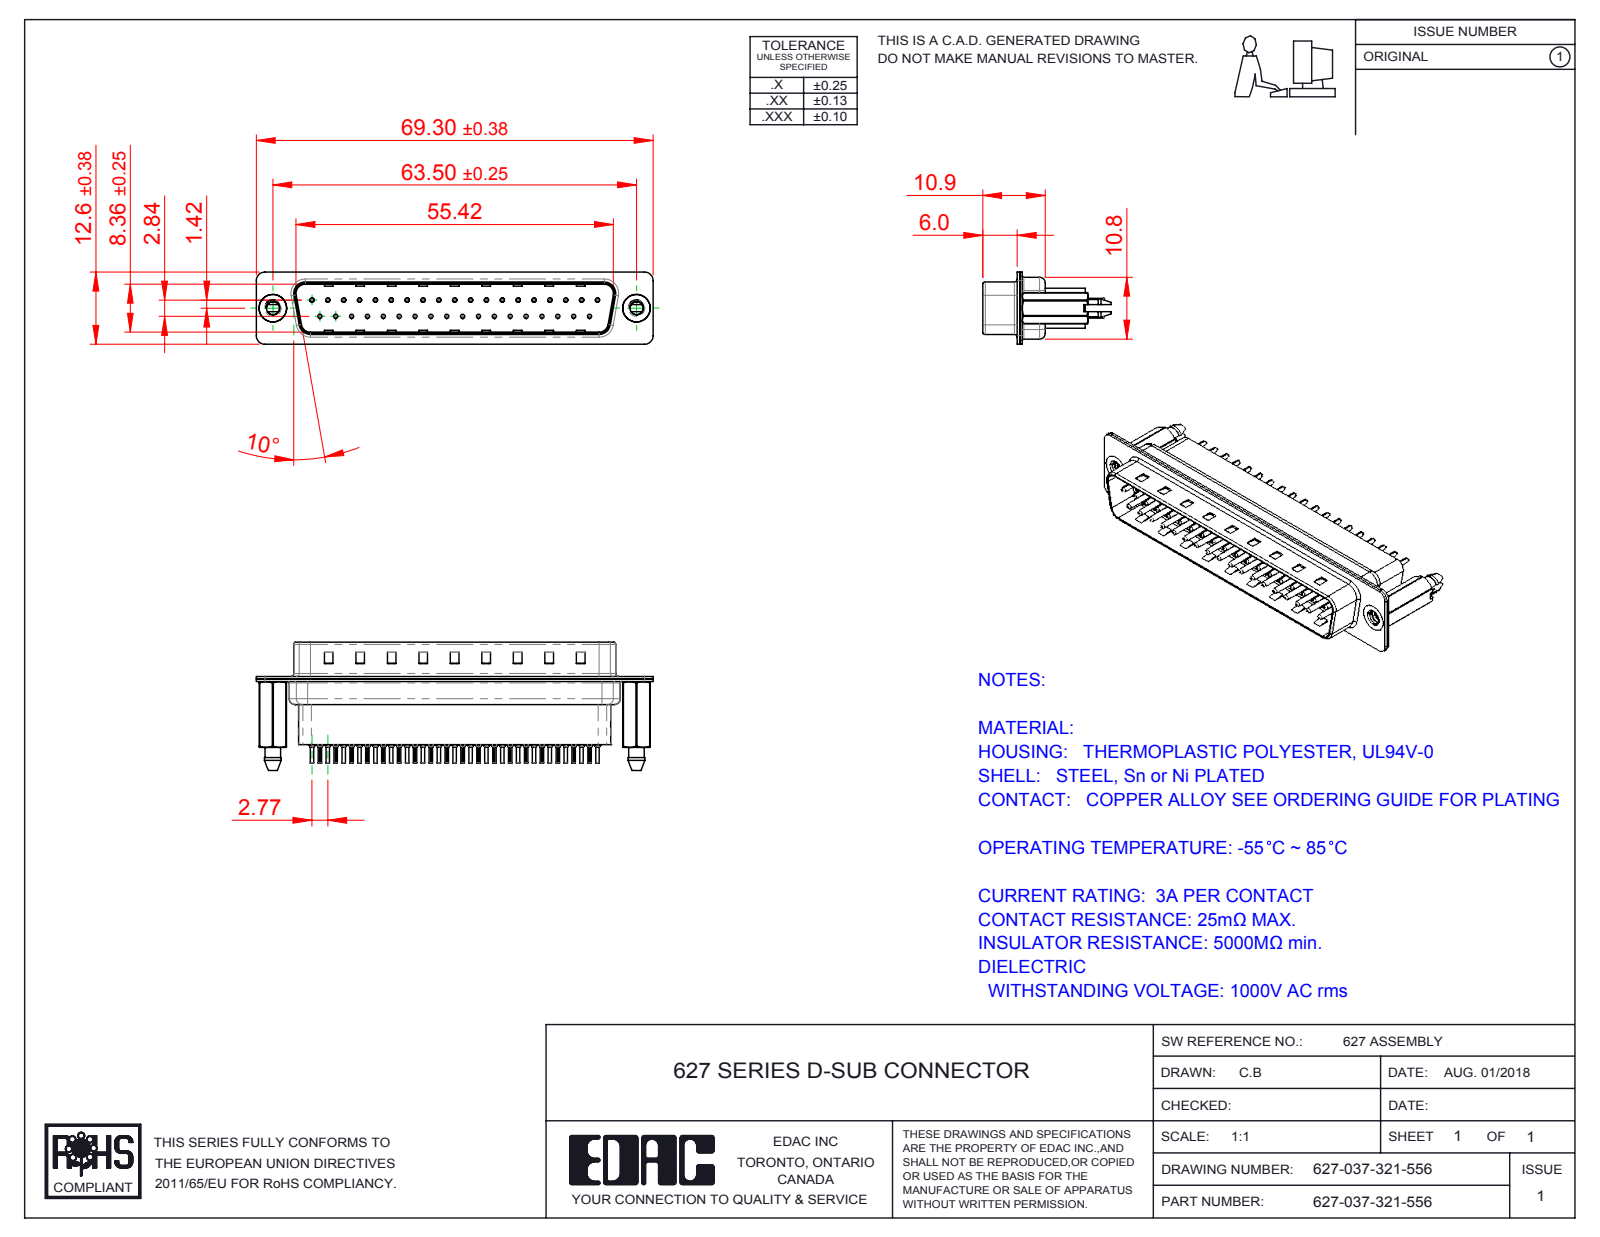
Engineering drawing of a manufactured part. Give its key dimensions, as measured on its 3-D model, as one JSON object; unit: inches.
{"part_name": "627 4-40 Threaded Boardlock_HP; 627 Contact Row 2_21H; 627 Shell Rear_37 Contacts; 627 Housing_37 HP (+3 more)", "step_written_by": "SolidWorks 2016 (CONFIG_CONTROL_DESIGN)", "units": "inches", "bodies": {"solids": 42, "faces": 4146, "planar": 1123, "cylindrical": 1576, "other": 1447}, "overall_size": [2.728, 0.882, 0.496], "volume_in3": 0.35, "surface_area_in2": 22.42, "round_holes": [[0.008, 37], [0.014, 37], [0.043, 37], [0.063, 37], [0.089, 2], [0.157, 2], [0.189, 2]], "round_bosses_or_shafts": [[0.079, 37], [0.059, 37], [0.03, 37], [0.024, 37], [0.193, 2]], "partial_cylinders_radius": [[0.004, 74], [0.059, 18], [0.079, 12], [0.063, 10], [0.02, 8], [0.01, 4], [0.024, 4], [0.026, 4]], "face_to_face_distances": [0.016, 0.032, 0.377, 0.027, 0.302, 0.018, 0.059, 0.043, 0.318, 0.345], "hole_center_spacings": [0.124, 0.109, 0.218, 0.327, 0.198, 0.398, 0.436, 0.503]}
